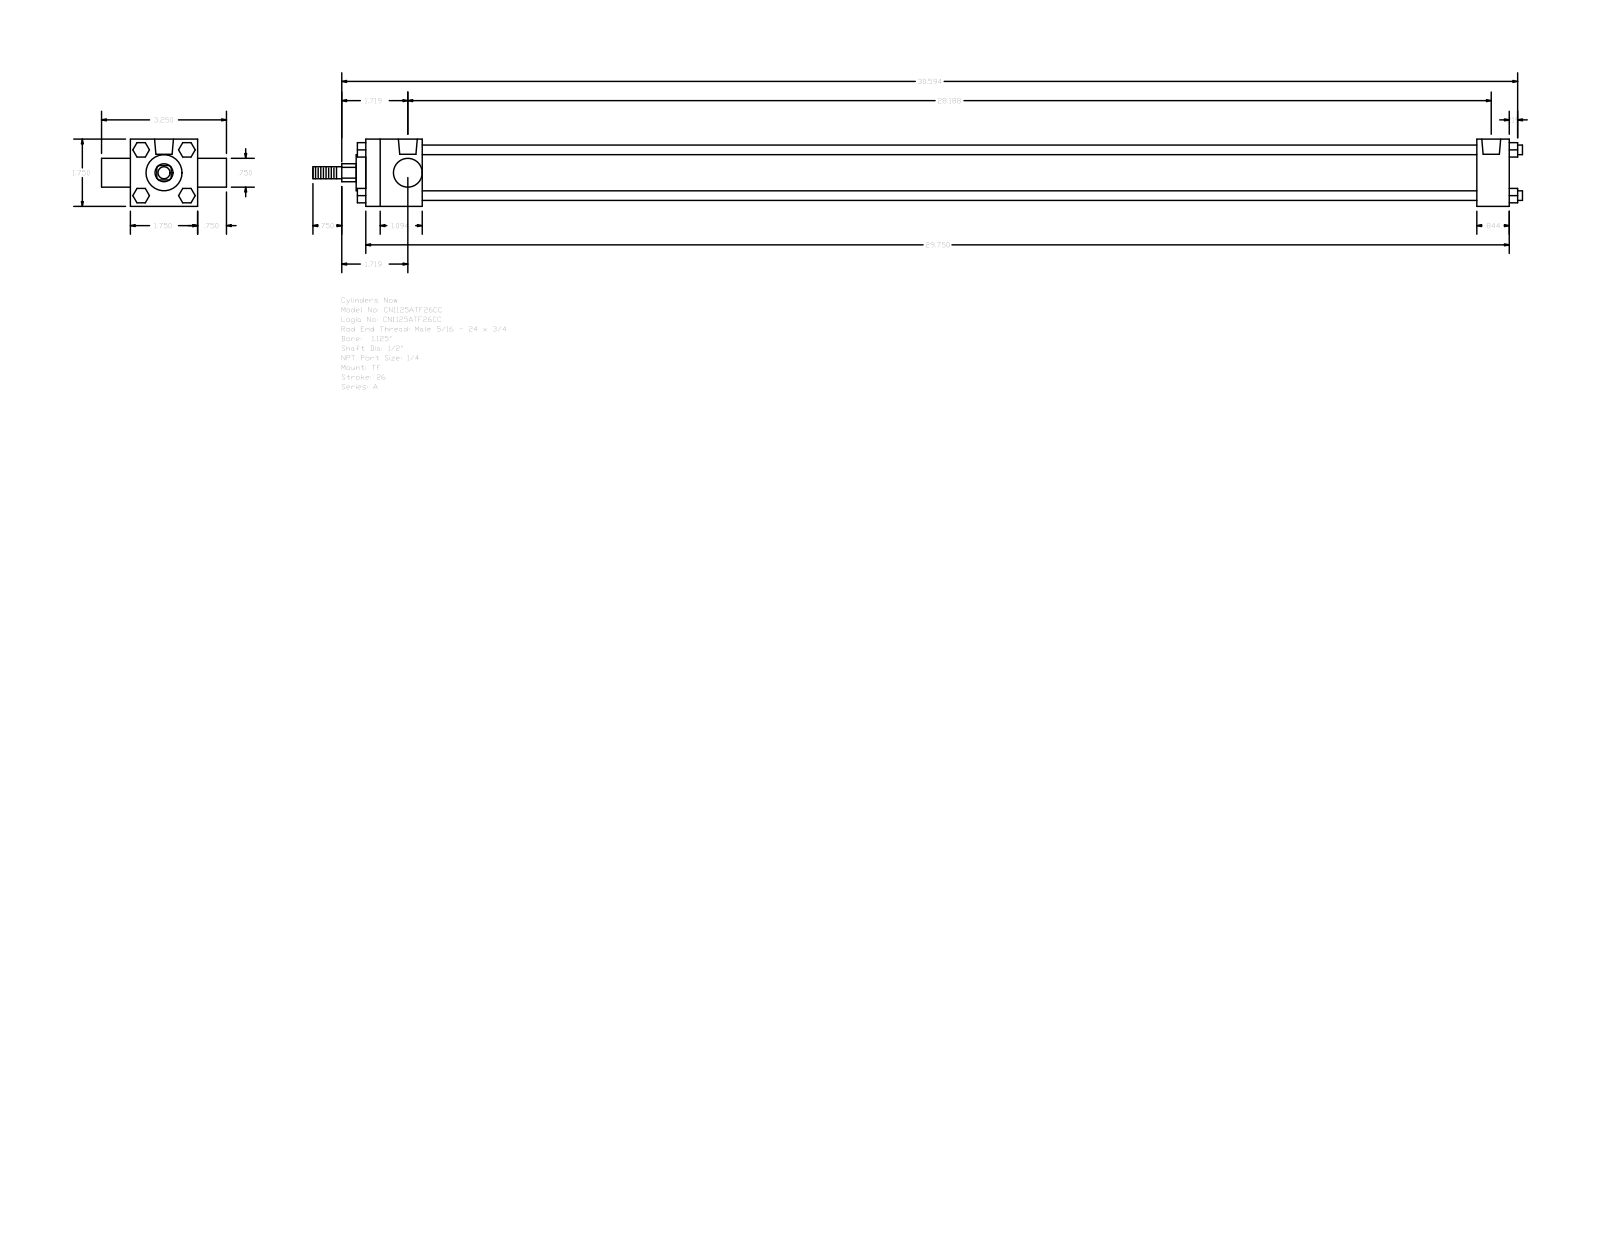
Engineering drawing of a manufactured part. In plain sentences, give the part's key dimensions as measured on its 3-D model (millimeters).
The part is named "A_TF__0112_0.5". Its 3-D file was written by "GSSL Pune (CONFIG_CONTROL_DESIGN)". It is 0 solids with 120 faces: 92 planar, 28 cylindrical and 0 other. Overall it measures 799.31 by 82.55 by 44.45 millimeters. Round holes: 3 of diameter 5.56, 2 of diameter 12.49. Round bosses or shafts: 4 of diameter 6.35, 1 of diameter 31.88, 1 of diameter 23.81, 1 of diameter 19.05, 1 of diameter 12.7, 1 of diameter 7.94. Partial cylindrical surfaces (rounded edges, fillets, slot ends): 1 of radius 5.94. The main face-to-face distances are 44.46, 755.64, 734.21, 21.43, 37.3, 696.91, 718.34, 19.04, 63.5, 9.53. The hole center spacings are 1.58, 1.59, 712.79, 714.37, 714.38, 715.96.
